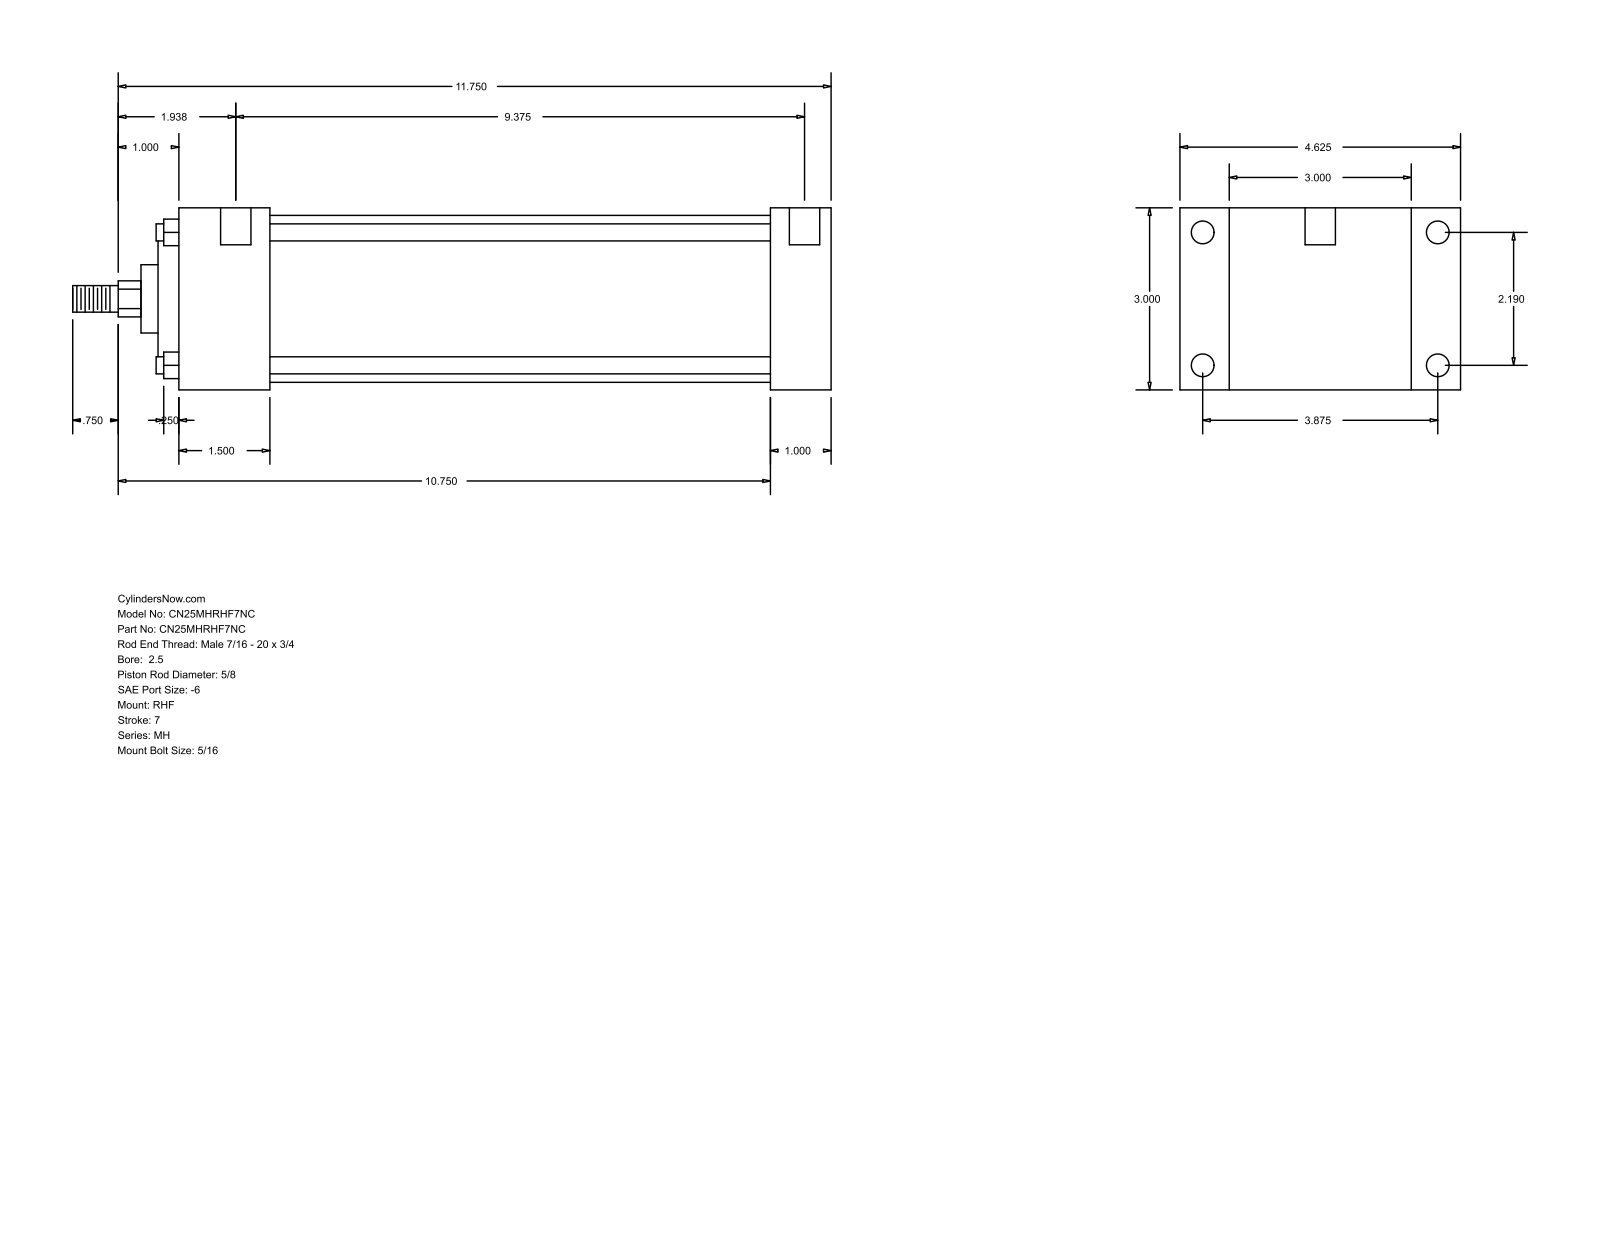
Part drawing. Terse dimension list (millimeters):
name: MH_RHF__0250_0.625
written by: GSSL Pune (CONFIG_CONTROL_DESIGN)
unit: mm
bodies: 0 solids, 90 faces (61 planar, 29 cylindrical, 0 other)
size: 317.5 × 117.47 × 76.2
holes: 4× ⌀5.56, 4× ⌀9.53, 2× ⌀12.7
bosses: 4× ⌀7.14, 1× ⌀69.85, 1× ⌀55.55, 1× ⌀28.57, 1× ⌀15.88, 1× ⌀11.11
rounds: 1× R7.54
face distances: 76.2, 25.4, 20.64, 96.84, 273.05, 247.65, 38.1, 117.48, 209.55, 234.95
hole spacings: 55.62, 98.42, 113.05, 246.06, 3.17, 4.76, 238.13, 241.3
